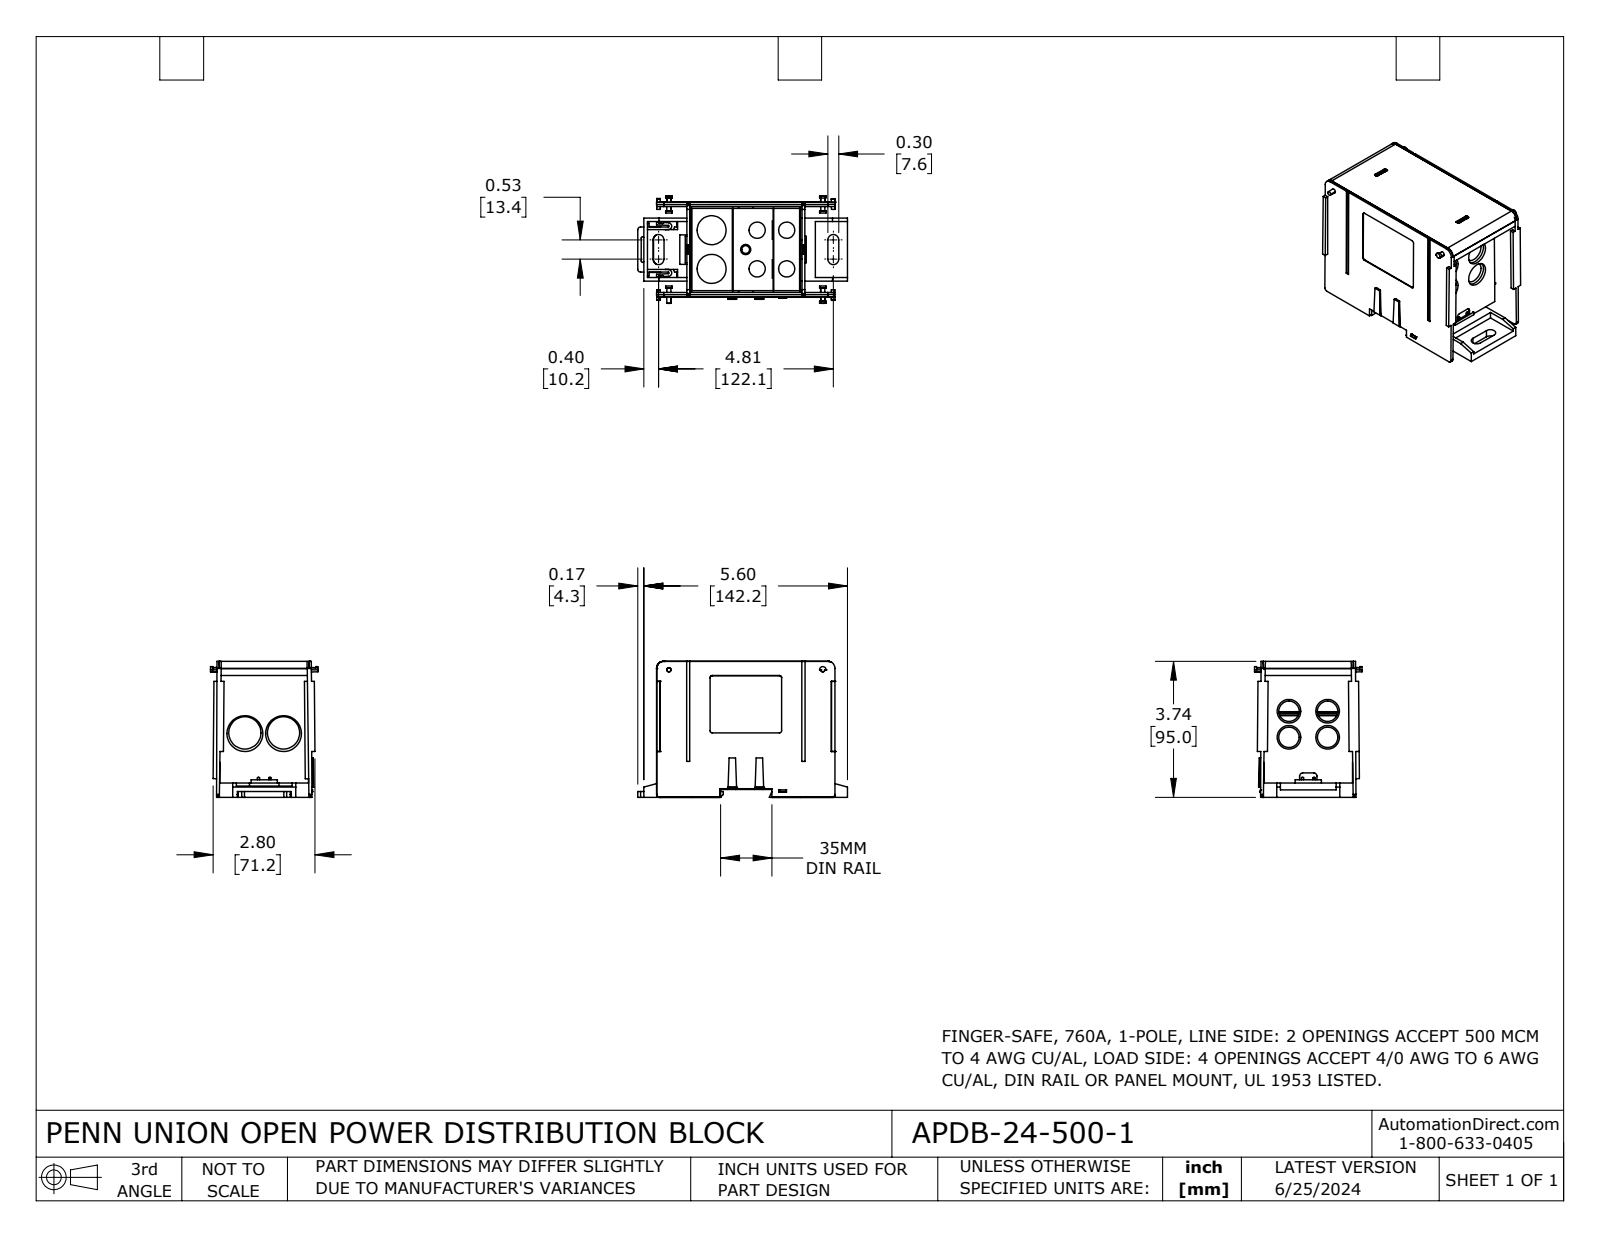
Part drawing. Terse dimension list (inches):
name: APDB-24-500-1
written by: SolidWorks 2023 (CONFIG_CONTROL_DESIGN)
unit: in
bodies: 13 solids, 824 faces (570 planar, 177 cylindrical, 77 other)
size: 5.77 × 3.741 × 2.955
volume: 20.9 in³; area: 245.9 in²
holes: 4× ⌀0.446, 4× ⌀0.559, 4× ⌀0.65, 2× ⌀0.798, 2× ⌀0.886, 2× ⌀0.984, 1× ⌀0.213, 1× ⌀0.28
rounds: 32× R0.02, 18× R0.059, 10× R0.039, 10× R0.079, 10× R0.197, 6× R0.012, 4× R0.089, 4× R0.15
face distances: 0.079, 3.169, 2.54, 0.071, 2.469, 0.02, 1.043, 3.248, 3.091, 1.201
hole spacings: 1.063, 0.02, 0.102, 0.122, 0.594, 0.614, 0.618, 0.717
